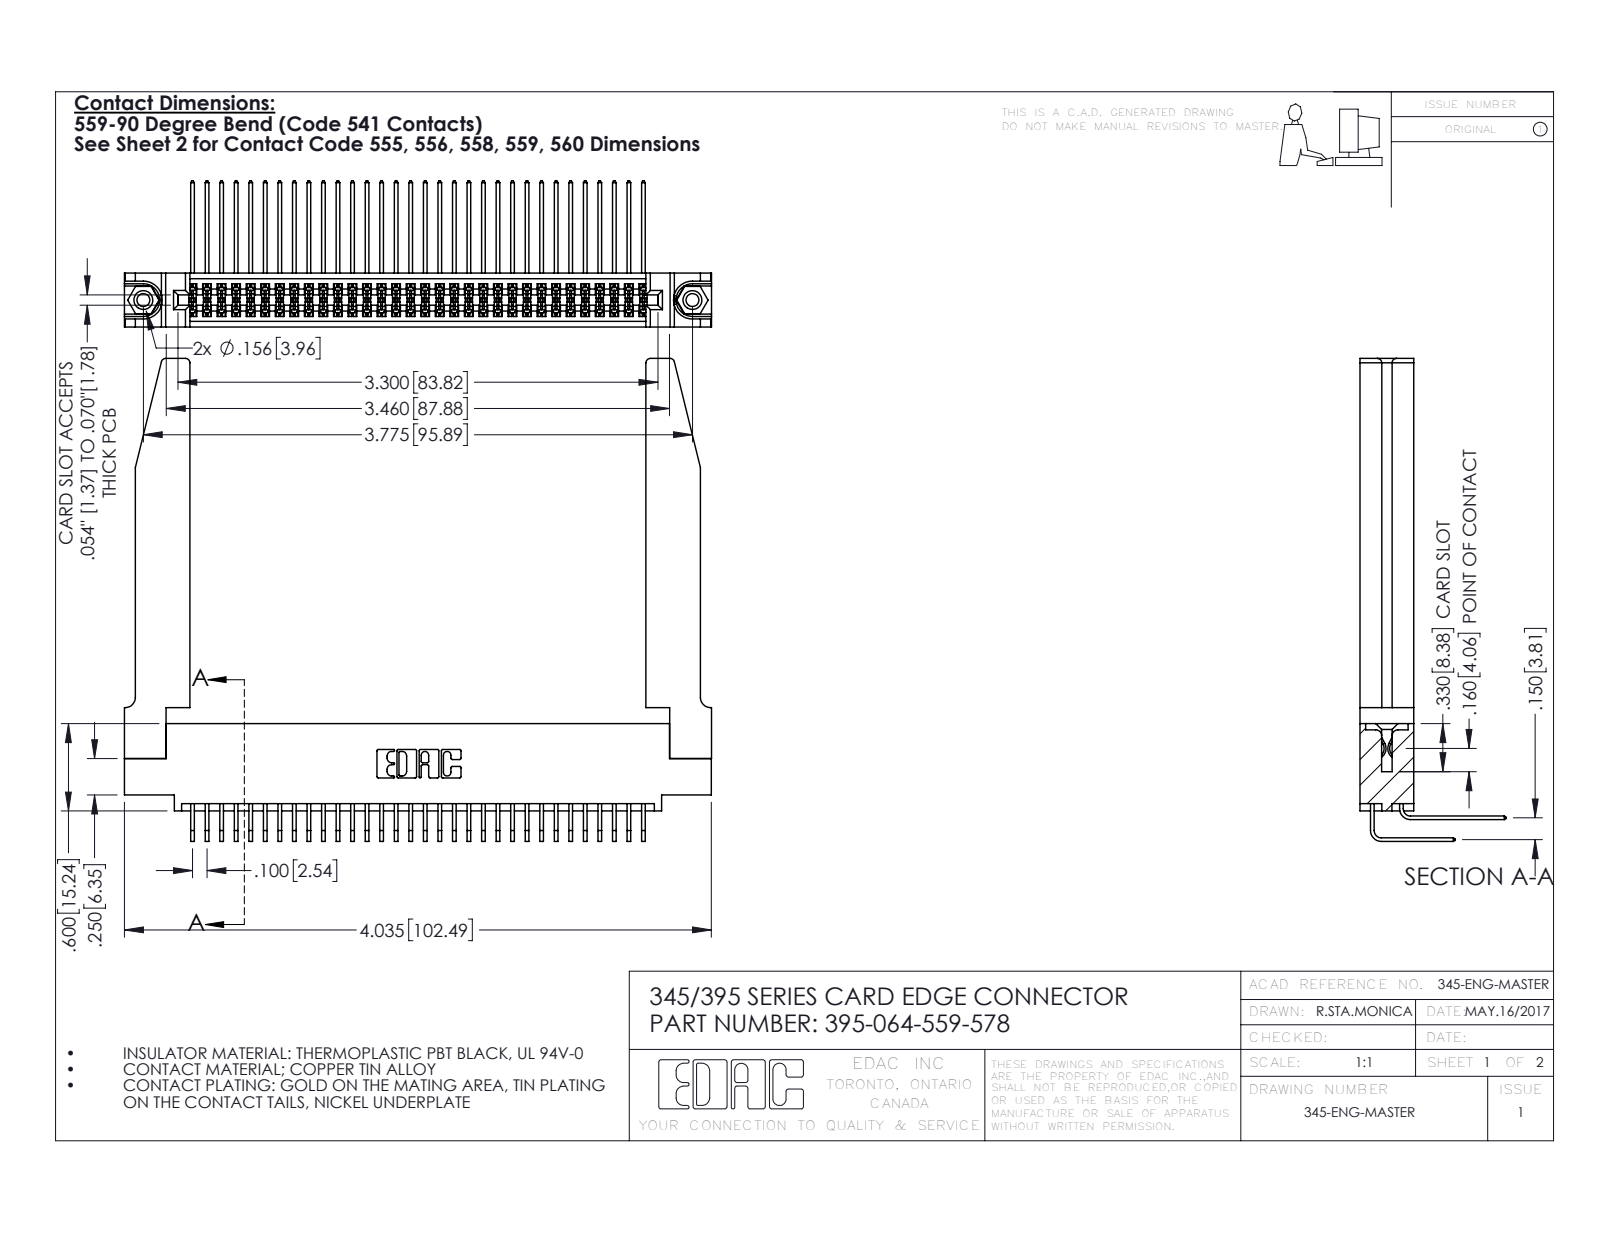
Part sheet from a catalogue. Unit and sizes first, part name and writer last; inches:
Units: inches
Overall size (bounding box): 4.036 × 3.319 × 1.005
Round holes (diameter × count): ⌀0.089 ×2, ⌀0.125 ×2, ⌀0.156 ×2, ⌀0.064 ×1
Round bosses / shafts (diameter × count): ⌀0.155 ×2
Partial cylindrical surfaces — rounded edges, fillets, slot ends (radius × count): R0.006 ×96, R0.01 ×22, R0.03 ×8, R0.007 ×6, R0.031 ×6, R0.026 ×3, R0.014 ×2, R0.019 ×2
Main face-to-face distances: 0.37, 0.072, 0.298, 0.2, 0.098, 0.272, 0.025, 0.225, 0.175, 0.15
Hole centre spacings: 0.27, 3.54, 3.775
Volume: 1.094 in³ · Surface area: 36.42 in²
Bodies: 69 solids, 3692 faces (2466 planar, 1174 cylindrical, 52 other)
Part name (STEP PRODUCT): 345-250-001_345-250-001-102; 395-064-559-578; 345-292-001_559 Tail - 2; 345-292-001_558 559 Tail - 1 (+2 more)
STEP written by: SolidWorks 2016 (CONFIG_CONTROL_DESIGN)
